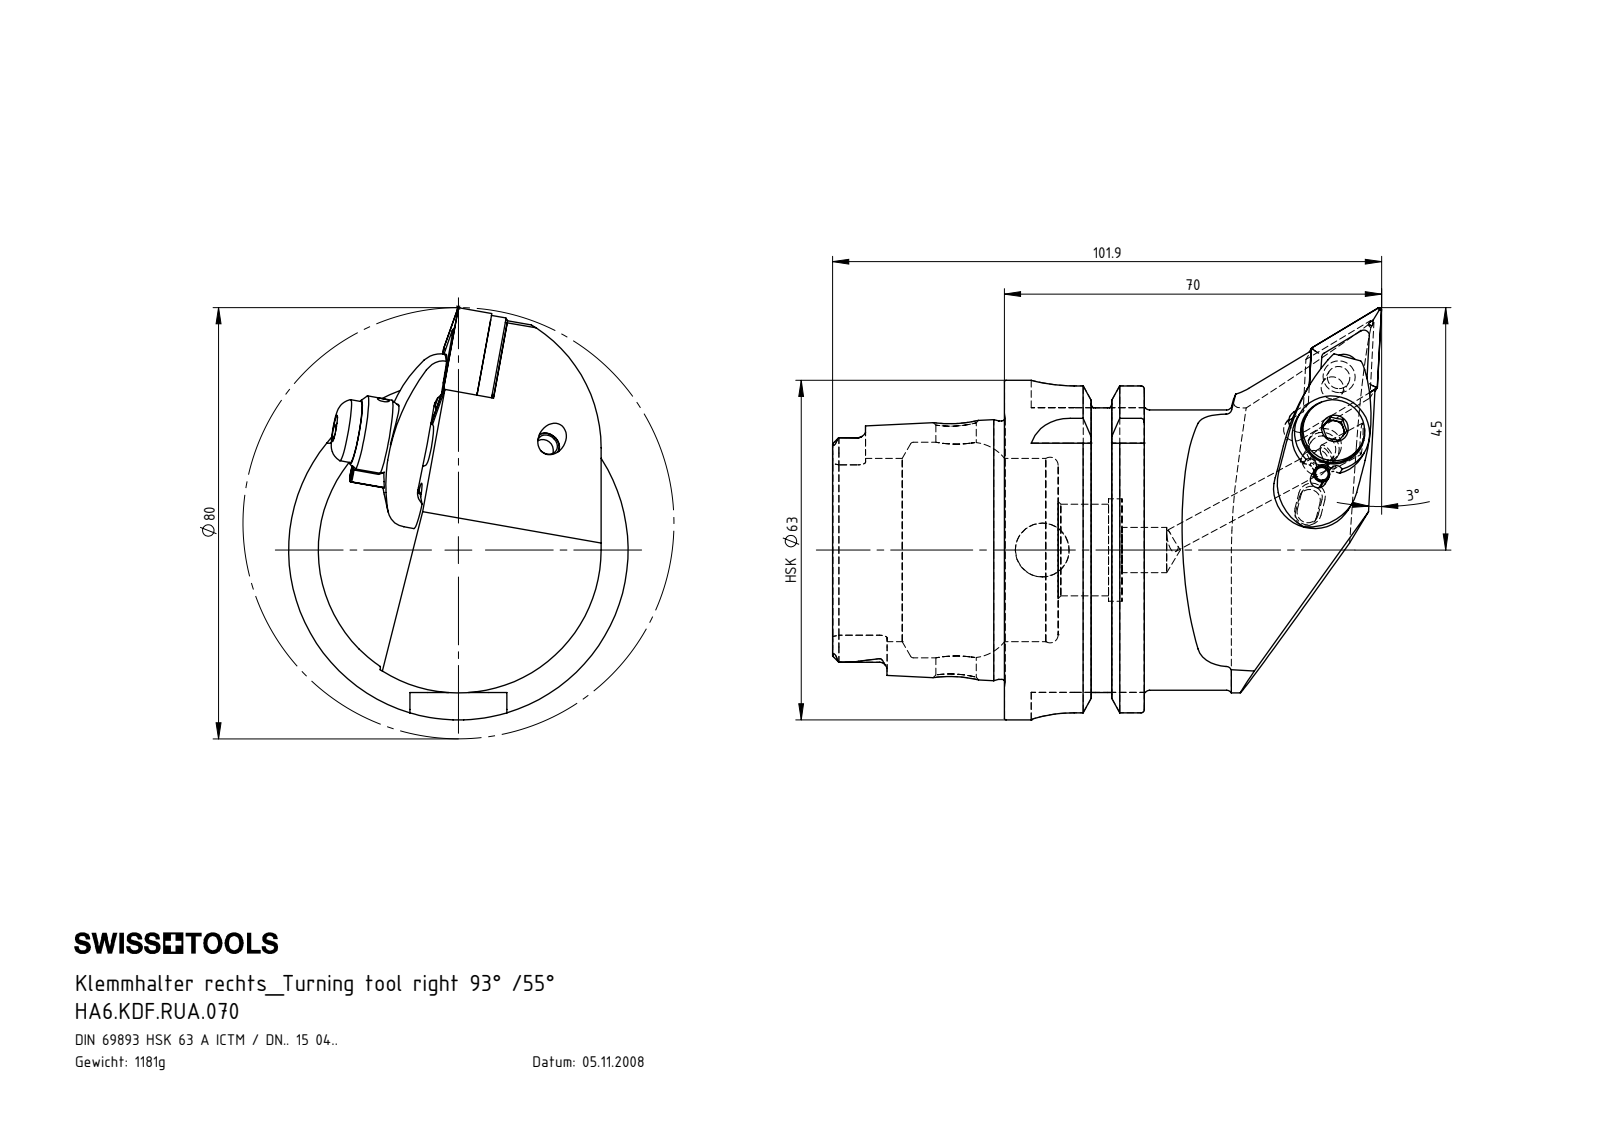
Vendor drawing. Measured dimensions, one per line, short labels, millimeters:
name: HA6.KDF.RUA.070; WCC-ER3.102.024_C; WDF-ER2.101.003_A; WCC-ER4.103.032_A (+7 more)
written by: SolidWorks 2017 (AUTOMOTIVE_DESIGN)
unit: mm
bodies: 12 solids, 477 faces (126 planar, 153 cylindrical, 198 other)
size: 101.9 × 76.5 × 63
volume: 151 370 mm³; area: 35 392 mm²
holes: 3× ⌀2, 2× ⌀4.2, 2× ⌀5, 2× ⌀7, 1× ⌀2.4, 1× ⌀3, 1× ⌀4, 1× ⌀5.16, 1× ⌀6.2, 1× ⌀6.5, 1× ⌀7.5, 1× ⌀8.4
bosses: 2× ⌀5, 2× ⌀3, 1× ⌀63, 1× ⌀54.95, 1× ⌀52, 1× ⌀47.94, 1× ⌀14, 1× ⌀11.5
rounds: 6× R0.39, 6× R0.69, 6× R1.4, 5× R0.4, 4× R8, 3× R1.5, 2× R2, 2× R2.82
face distances: 25.95, 16, 9.95, 12.32, 31.9, 41.85, 57.85, 6.01, 12.7, 52.8
hole spacings: 7.99, 8.01, 8.2, 23, 14.8, 14.81, 14.99, 15
